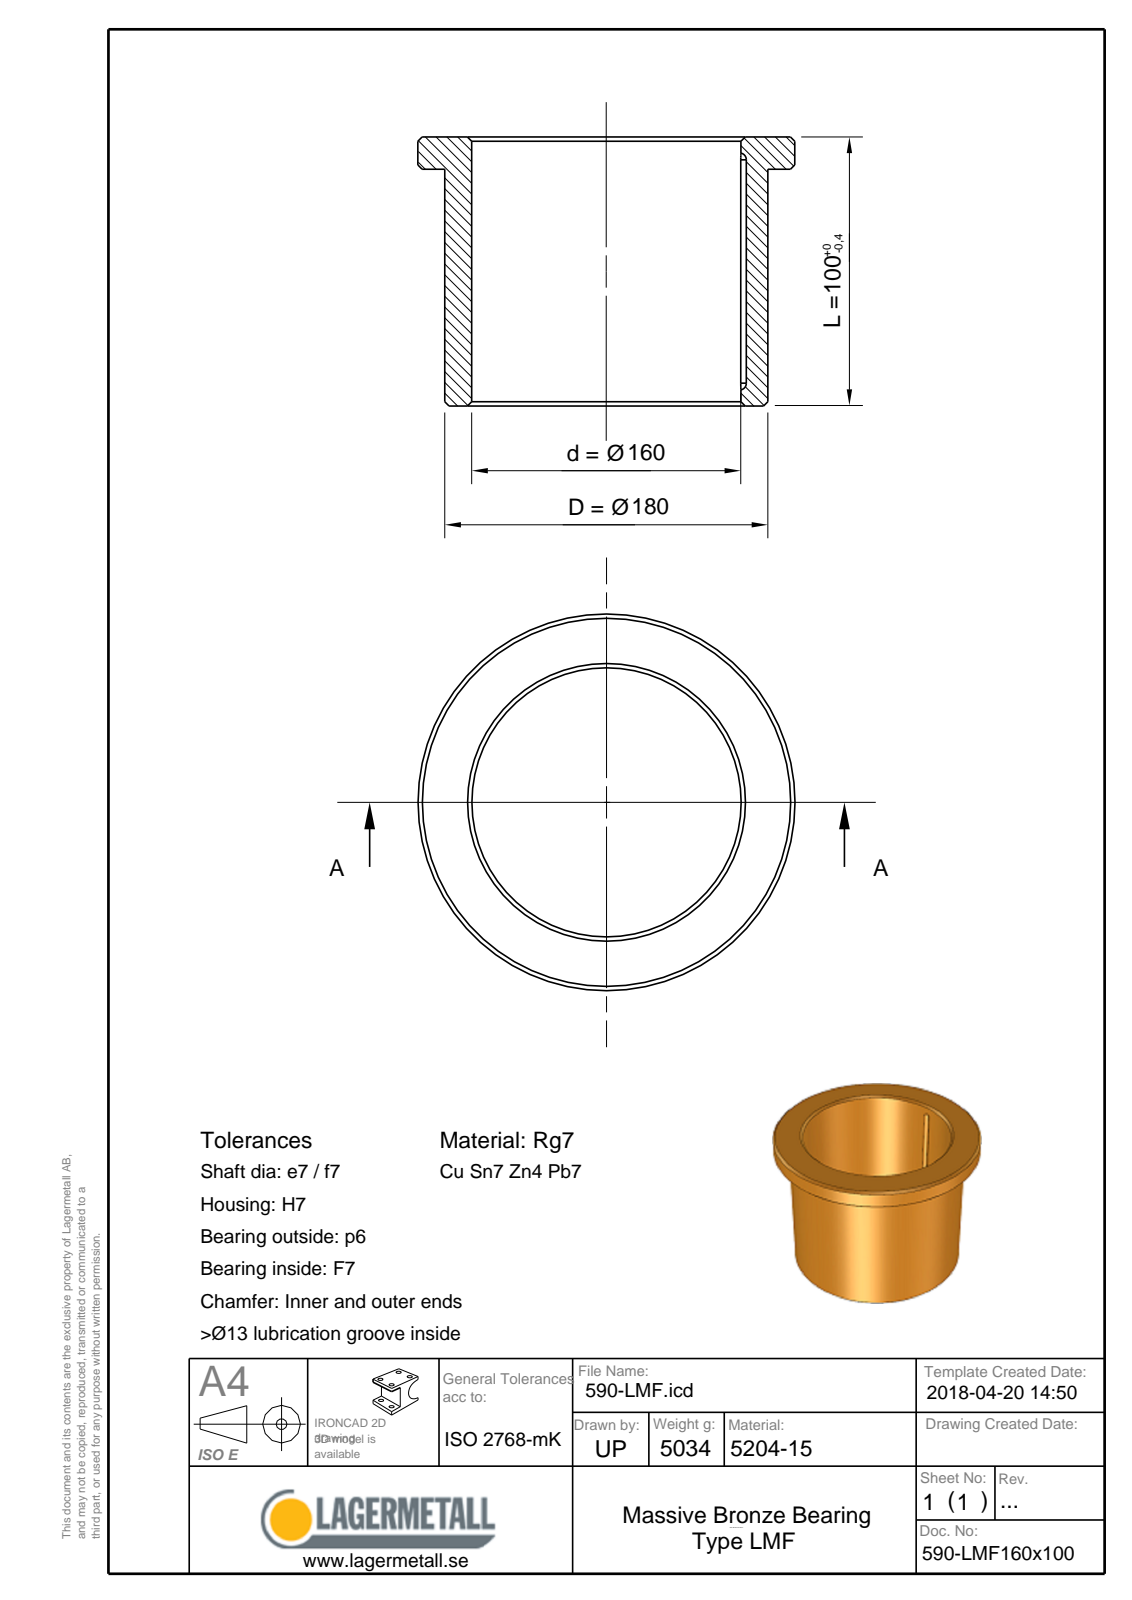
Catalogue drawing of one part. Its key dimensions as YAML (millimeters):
part_name: "590-LMF160x100"
step_written_by: "Spatial InterOp 3D (CONFIG_CONTROL_DESIGN)"
units: millimeters
bodies: {solids: 1, faces: 16, planar: 4, cylindrical: 5, other: 7}
overall_size: [195, 195, 100]
volume: 572054
surface_area: 123718
round_holes:
  - {diameter: 160, count: 1}
round_bosses_or_shafts:
  - {diameter: 195, count: 1}
  - {diameter: 180, count: 1}
partial_cylinders:
  - {radius: 2.25, count: 2}
face_to_face_distances: [10, 90, 100]
